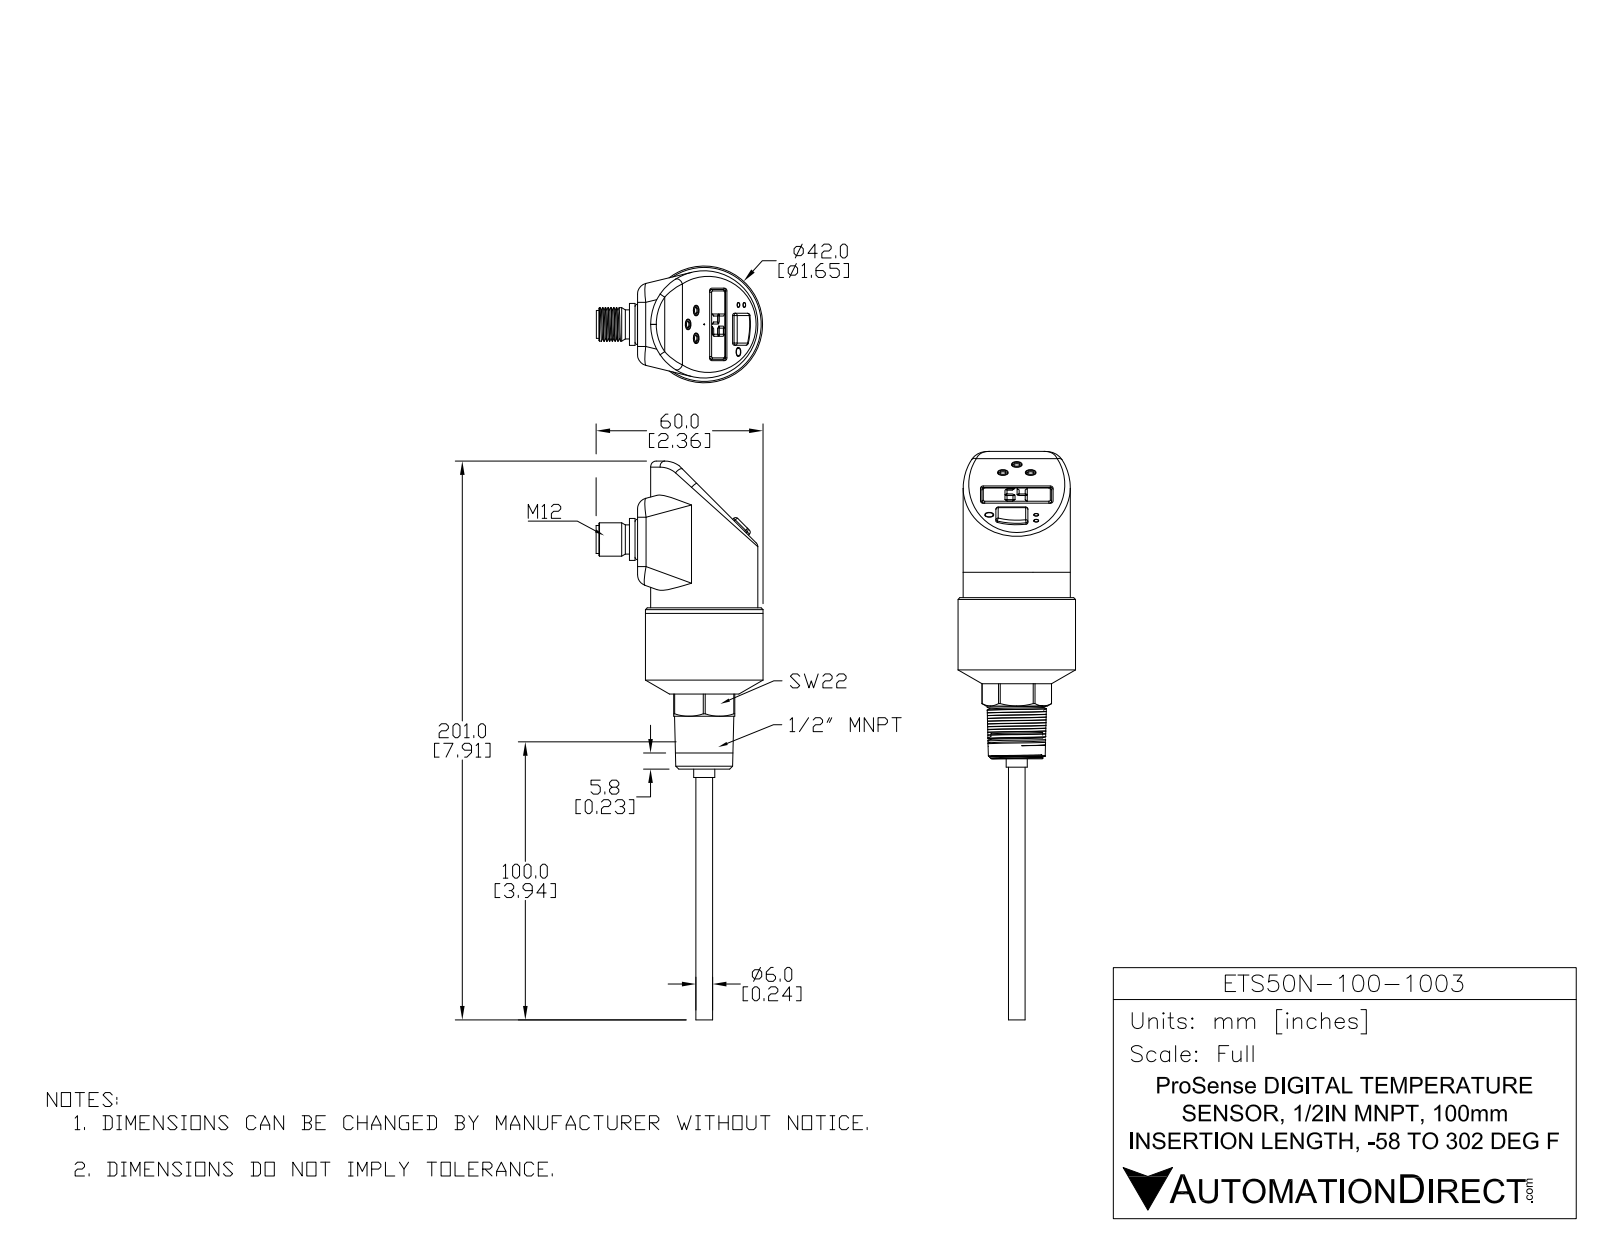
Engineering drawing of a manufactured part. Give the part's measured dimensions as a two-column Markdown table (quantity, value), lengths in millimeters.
| quantity | value |
| --- | --- |
| part name | ETS50N-100-1003 |
| STEP written by | SolidWorks 2016 (AUTOMOTIVE_DESIGN) |
| units | millimeters |
| bodies | 1 solid, 324 faces (138 planar, 95 cylindrical, 91 other) |
| overall size | 204.49 × 59.95 × 42.3 |
| volume | 109 158 mm³ |
| surface area | 19 661 mm² |
| round holes (diameter × count) | 8.45 × 1, 11 × 1 |
| round bosses / shafts (diameter × count) | 1.4 × 4, 1 × 4, 42.3 × 1, 38.55 × 1, 15.1 × 1, 14.56 × 1, 12 × 1, 10.5 × 1 |
| partial cylindrical surfaces (radius × count) | 1 × 8, 0.8 × 7, 0.5 × 4, 3.99 × 4, 7 × 4, 0.61 × 1, 2 × 1, 9.01 × 1 |
| main face-to-face distances | 22, 57.99, 13.9, 13, 0.9, 2, 2.9, 15.9, 37.9, 35 |
